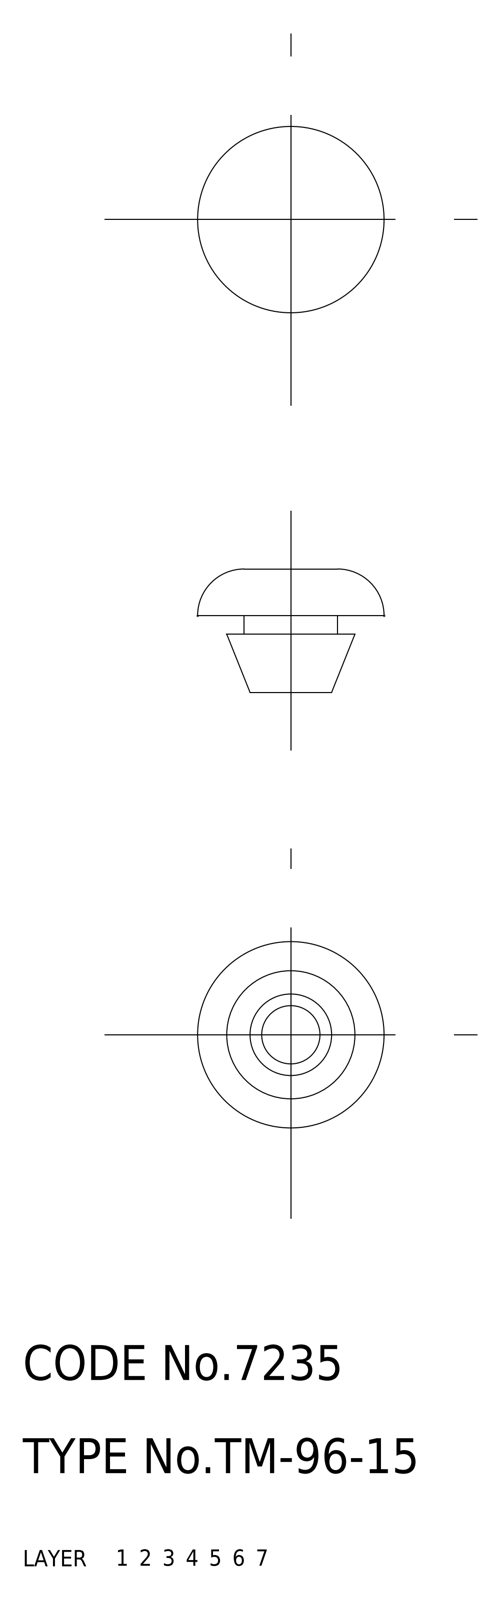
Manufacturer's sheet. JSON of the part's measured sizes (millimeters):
{"part_name": "cushion", "step_written_by": "CADfix (AUTOMOTIVE_DESIGN)", "units": "millimeters", "bodies": {"solids": 1, "faces": 13, "planar": 0, "cylindrical": 0, "other": 13}, "overall_size": [16, 16, 10.6], "volume_mm3": 926, "surface_area_mm2": 839}
